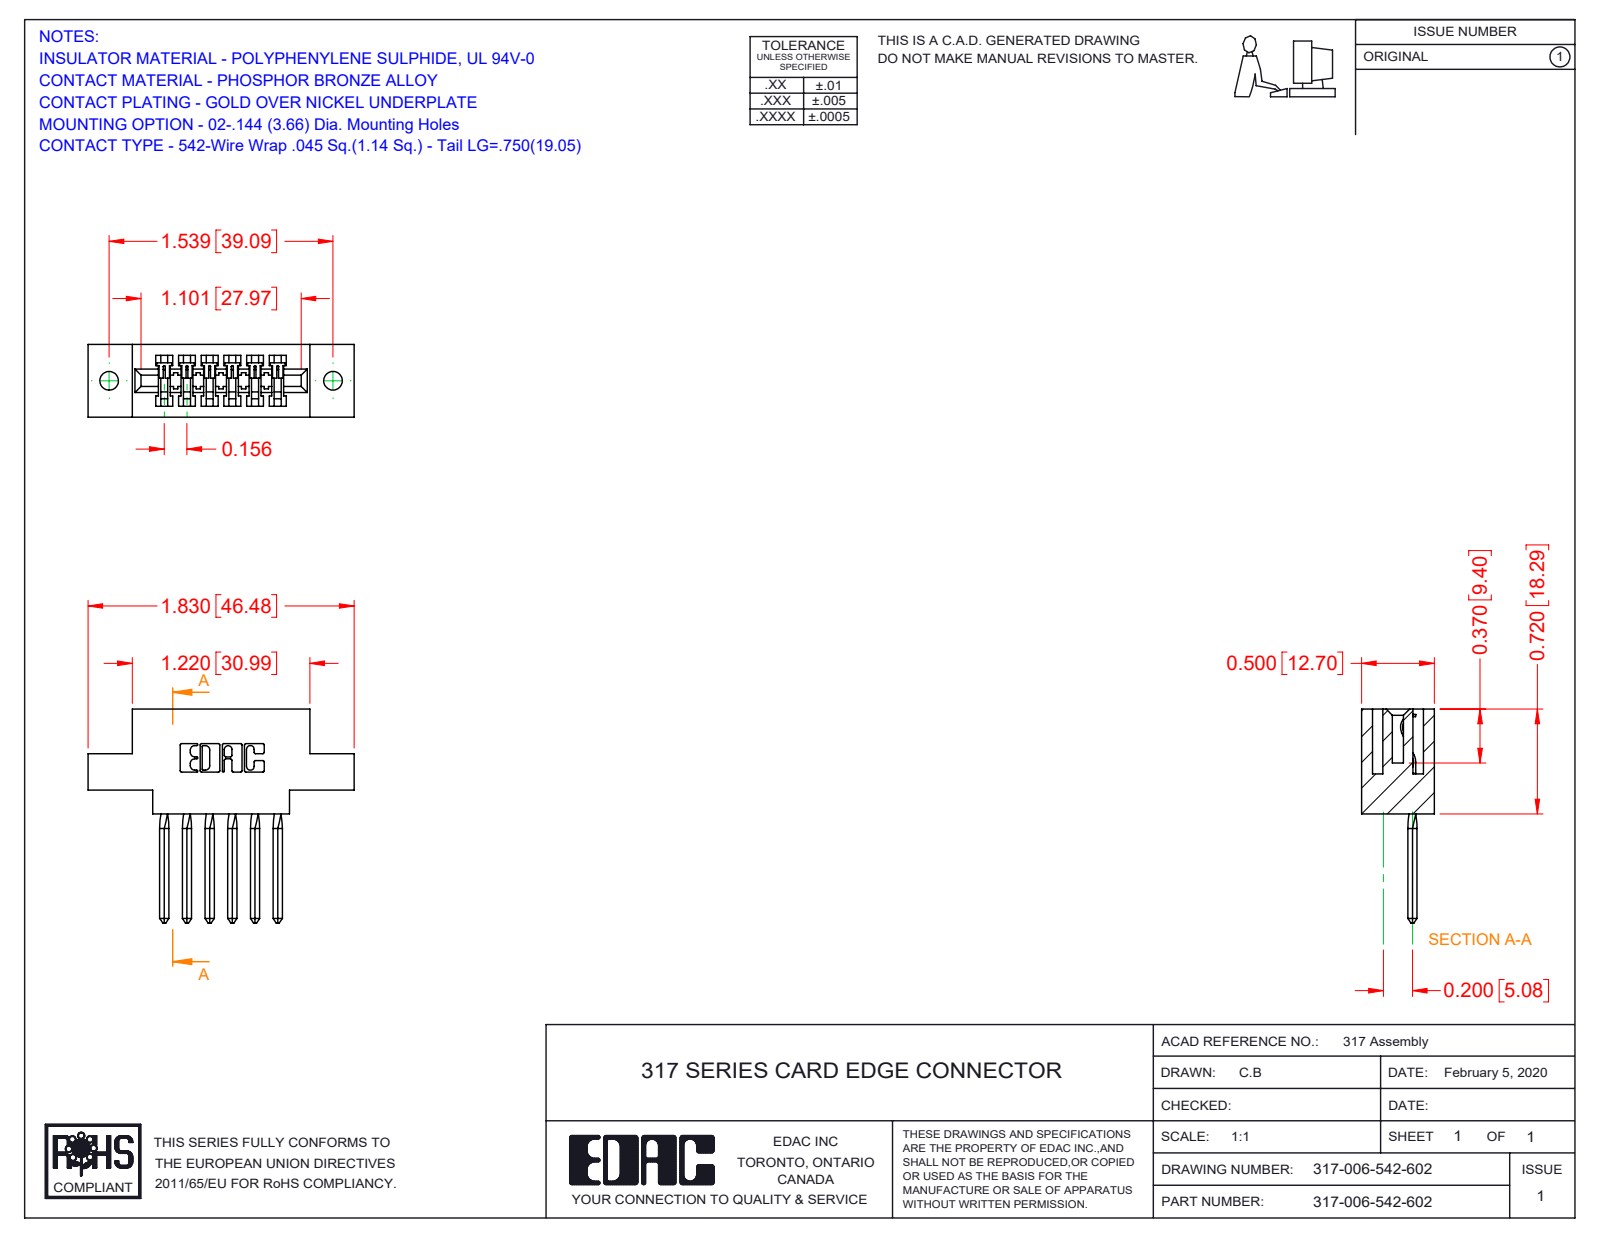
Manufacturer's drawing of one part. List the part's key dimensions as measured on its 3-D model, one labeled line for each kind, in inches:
Part name (STEP PRODUCT): 317-006-542-602; 317-290-003_542; 317 Part_.144 Dia
STEP written by: SolidWorks 2016 (CONFIG_CONTROL_DESIGN)
Units: inches
Bodies: 7 solids, 552 faces (442 planar, 86 cylindrical, 24 other)
Overall size (bounding box): 1.83 × 1.47 × 0.5
Volume: 0.378 in³ · Surface area: 10.03 in²
Round holes (diameter × count): ⌀0.128 ×2
Partial cylindrical surfaces — rounded edges, fillets, slot ends (radius × count): R0.01 ×22, R0.006 ×12, R0.007 ×6, R0.031 ×6, R0.026 ×3, R0.074 ×1, R0.089 ×1, R0.1 ×1
Main face-to-face distances: 0.5, 0.075, 0.425, 0.156, 0.11, 0.065, 0.116, 0.163, 0.136, 0.305
Hole centre spacings: 1.539
